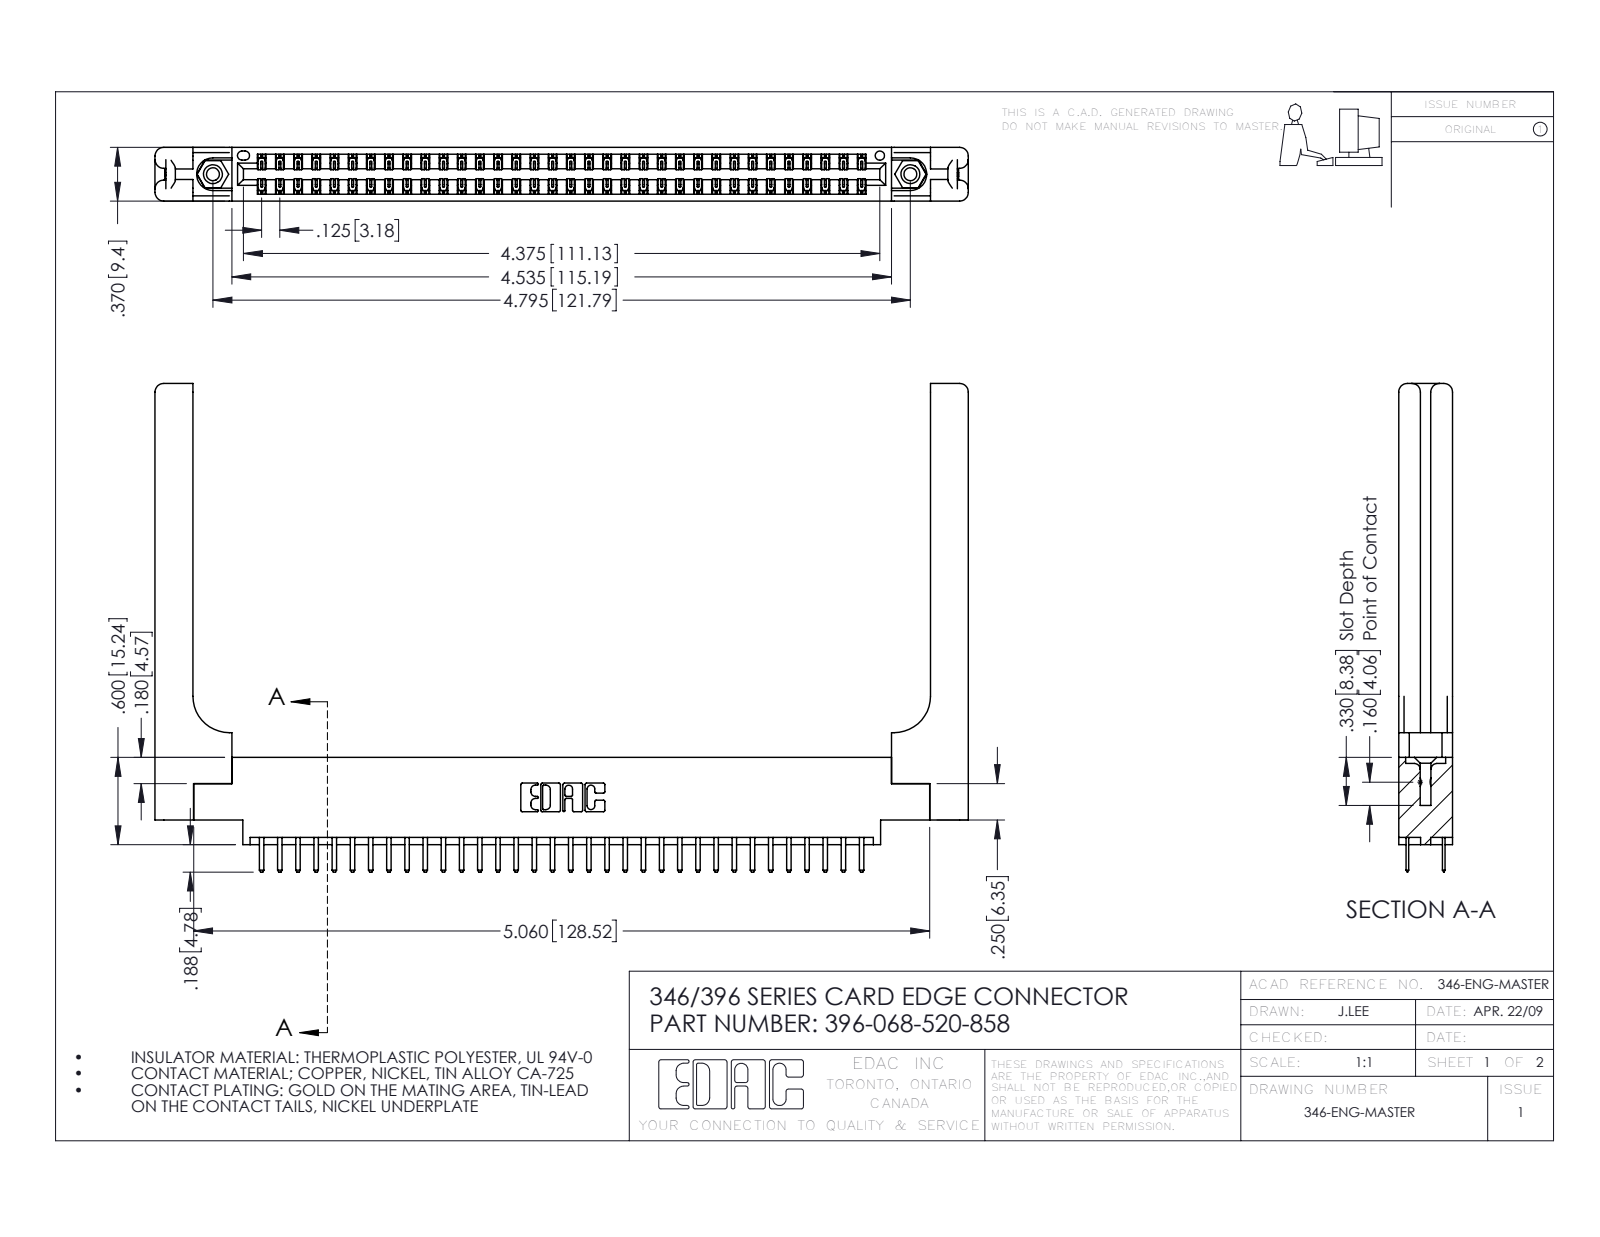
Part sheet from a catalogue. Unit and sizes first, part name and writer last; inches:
Units: inches
Overall size (bounding box): 5.591 × 3.358 × 0.37
Round holes (diameter × count): ⌀0.089 ×2, ⌀0.125 ×2, ⌀0.156 ×2, ⌀0.064 ×1
Round bosses / shafts (diameter × count): ⌀0.155 ×2
Partial cylindrical surfaces — rounded edges, fillets, slot ends (radius × count): R0.006 ×102, R0.01 ×72, R0.01 ×22, R0.06 ×16, R0.007 ×6, R0.031 ×6, R0.026 ×3, R0.014 ×2
Main face-to-face distances: 0.37, 0.048, 0.322, 0.072, 0.148, 0.15, 0.25, 0.298, 0.025, 0.275
Hole centre spacings: 0.246, 4.587, 4.795
Volume: 1.287 in³ · Surface area: 36.66 in²
Bodies: 73 solids, 4190 faces (2744 planar, 1386 cylindrical, 60 other)
Part name (STEP PRODUCT): 345-292-001_345-293-120; 346 Part_0.170 Offset - 0.156 Dia-TH; 396-068-520-858; 346-220-058_345-220-058 (+1 more)
STEP written by: SolidWorks 2016 (CONFIG_CONTROL_DESIGN)
